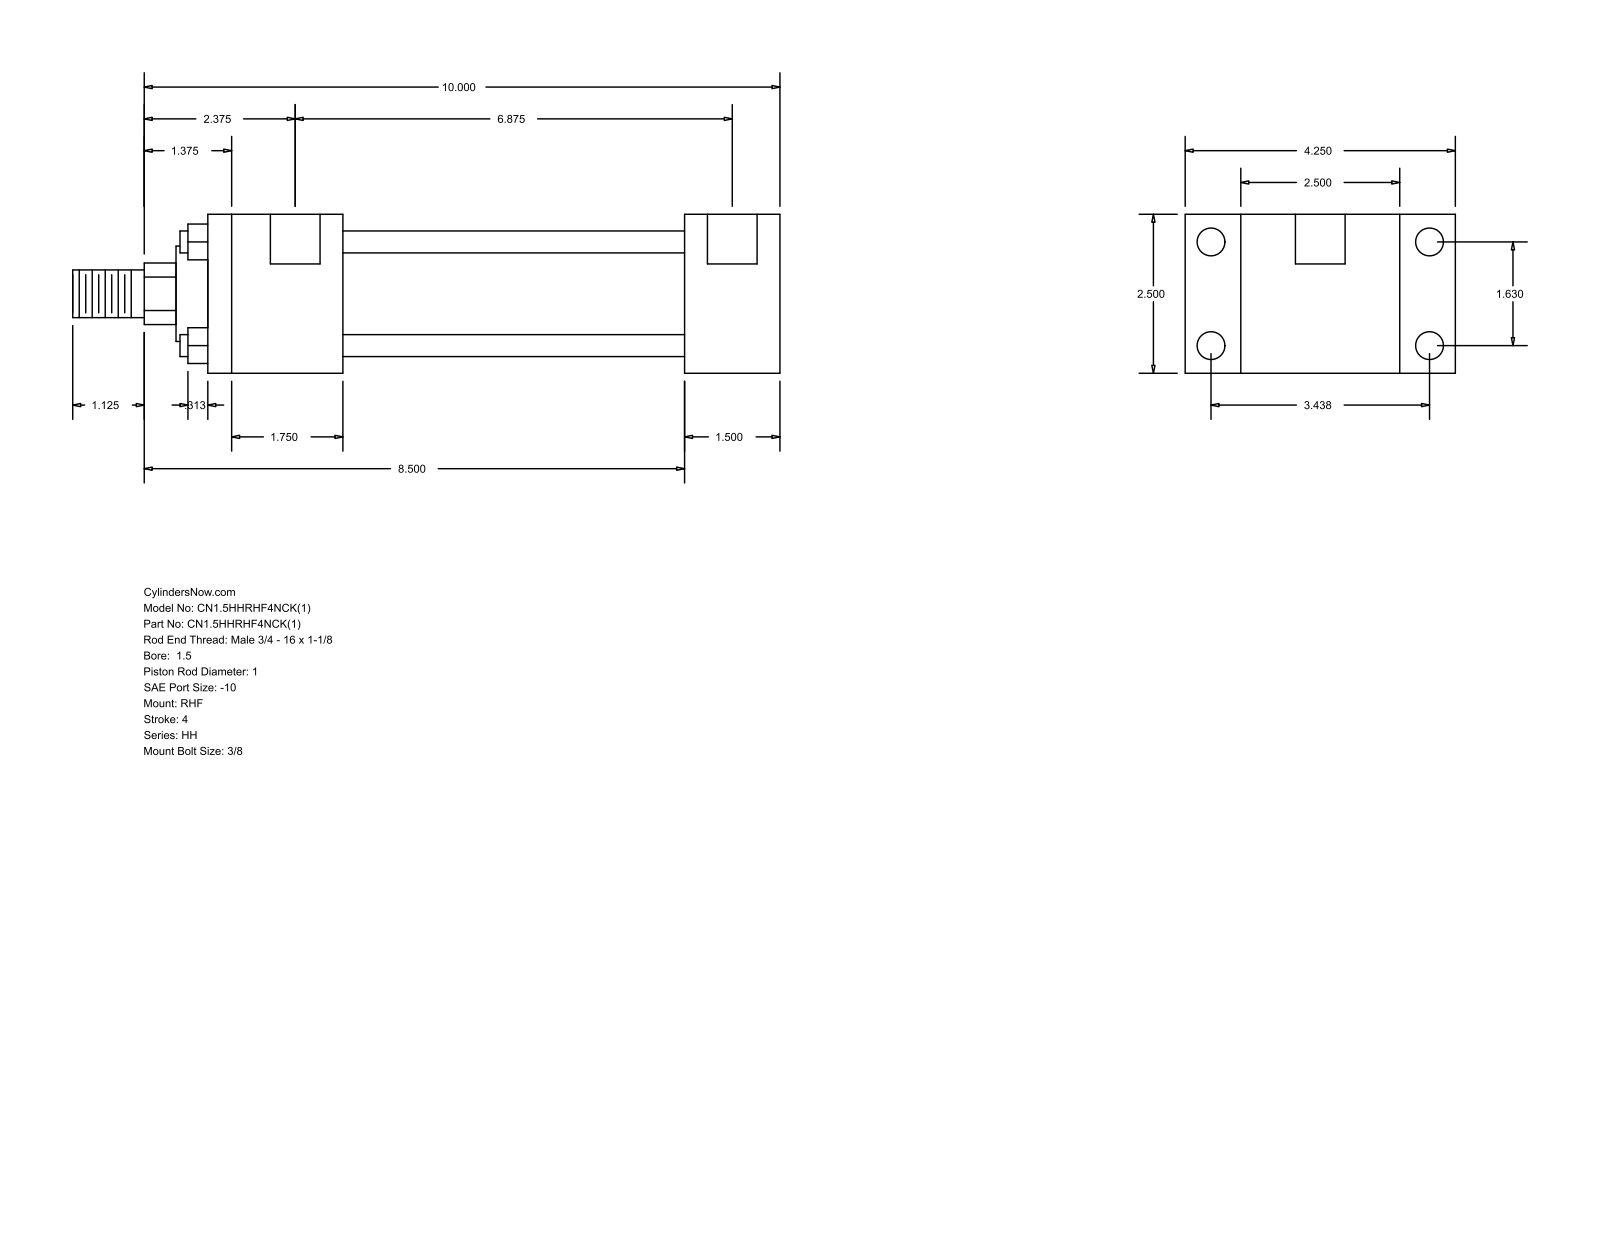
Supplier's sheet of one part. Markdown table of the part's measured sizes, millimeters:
| quantity | value |
| --- | --- |
| part name | HH_RHF__0150_1 |
| STEP written by | GSSL Pune (CONFIG_CONTROL_DESIGN) |
| units | millimeters |
| bodies | 0 solids, 88 faces (60 planar, 28 cylindrical, 0 other) |
| overall size | 282.57 × 107.95 × 63.5 |
| round holes (diameter × count) | 5.56 × 4, 11.13 × 4, 19.84 × 2 |
| round bosses / shafts (diameter × count) | 8.76 × 4, 44.45 × 1, 38.1 × 1, 25.4 × 1, 19.05 × 1 |
| partial cylindrical surfaces (radius × count) | 12.29 × 1 |
| main face-to-face distances | 63.5, 22.23, 85.73, 38.1, 107.96, 136.52, 174.62, 53.98, 190.5, 228.6 |
| hole center spacings | 1.59, 41.4, 87.32, 96.64, 176.21, 177.8, 174.62 |
